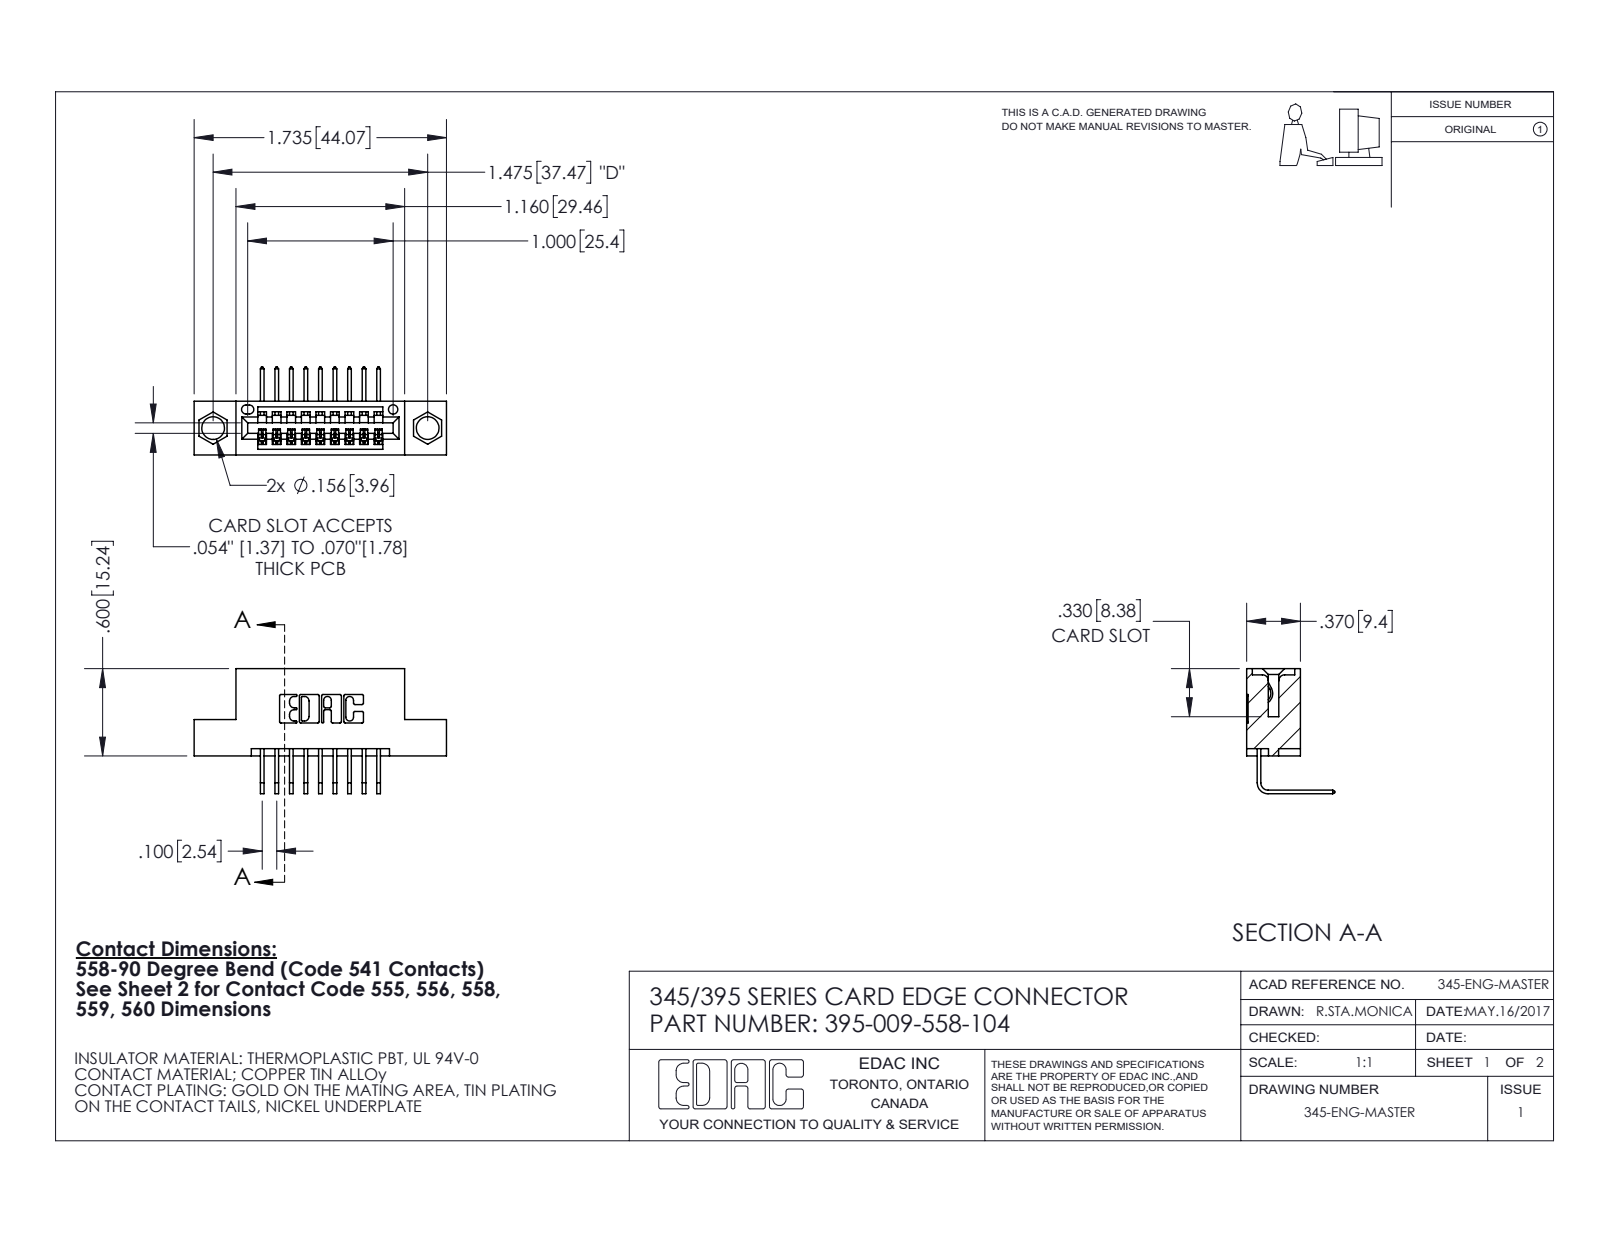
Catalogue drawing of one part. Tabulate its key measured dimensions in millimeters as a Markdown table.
| quantity | value |
| --- | --- |
| part name | 345 Part_Flush Mounting Lugs - 0.156 Dia-TI; 345-292-001_558 Tail - 2; 395-009-558-104 |
| STEP written by | SolidWorks 2020 (CONFIG_CONTROL_DESIGN) |
| units | millimeters |
| bodies | 10 solids, 680 faces (472 planar, 208 cylindrical, 0 other) |
| overall size | 44.1 × 21.8 × 15.4 |
| volume | 3 830 mm³ |
| surface area | 4 672 mm² |
| round holes (diameter × count) | 4 × 2, 1.6 × 1 |
| partial cylindrical surfaces (radius × count) | 0.3 × 22, 0.2 × 18, 0.2 × 6, 0.8 × 6, 0.7 × 3, 0.8 × 2, 1 × 2, 0.4 × 1 |
| main face-to-face distances | 5.1, 9.4, 1.8, 7.6, 2.5, 2.5, 6.9, 0.6, 15.2, 1.5 |
| hole center spacings | 6.9, 31.6, 37.5 |
